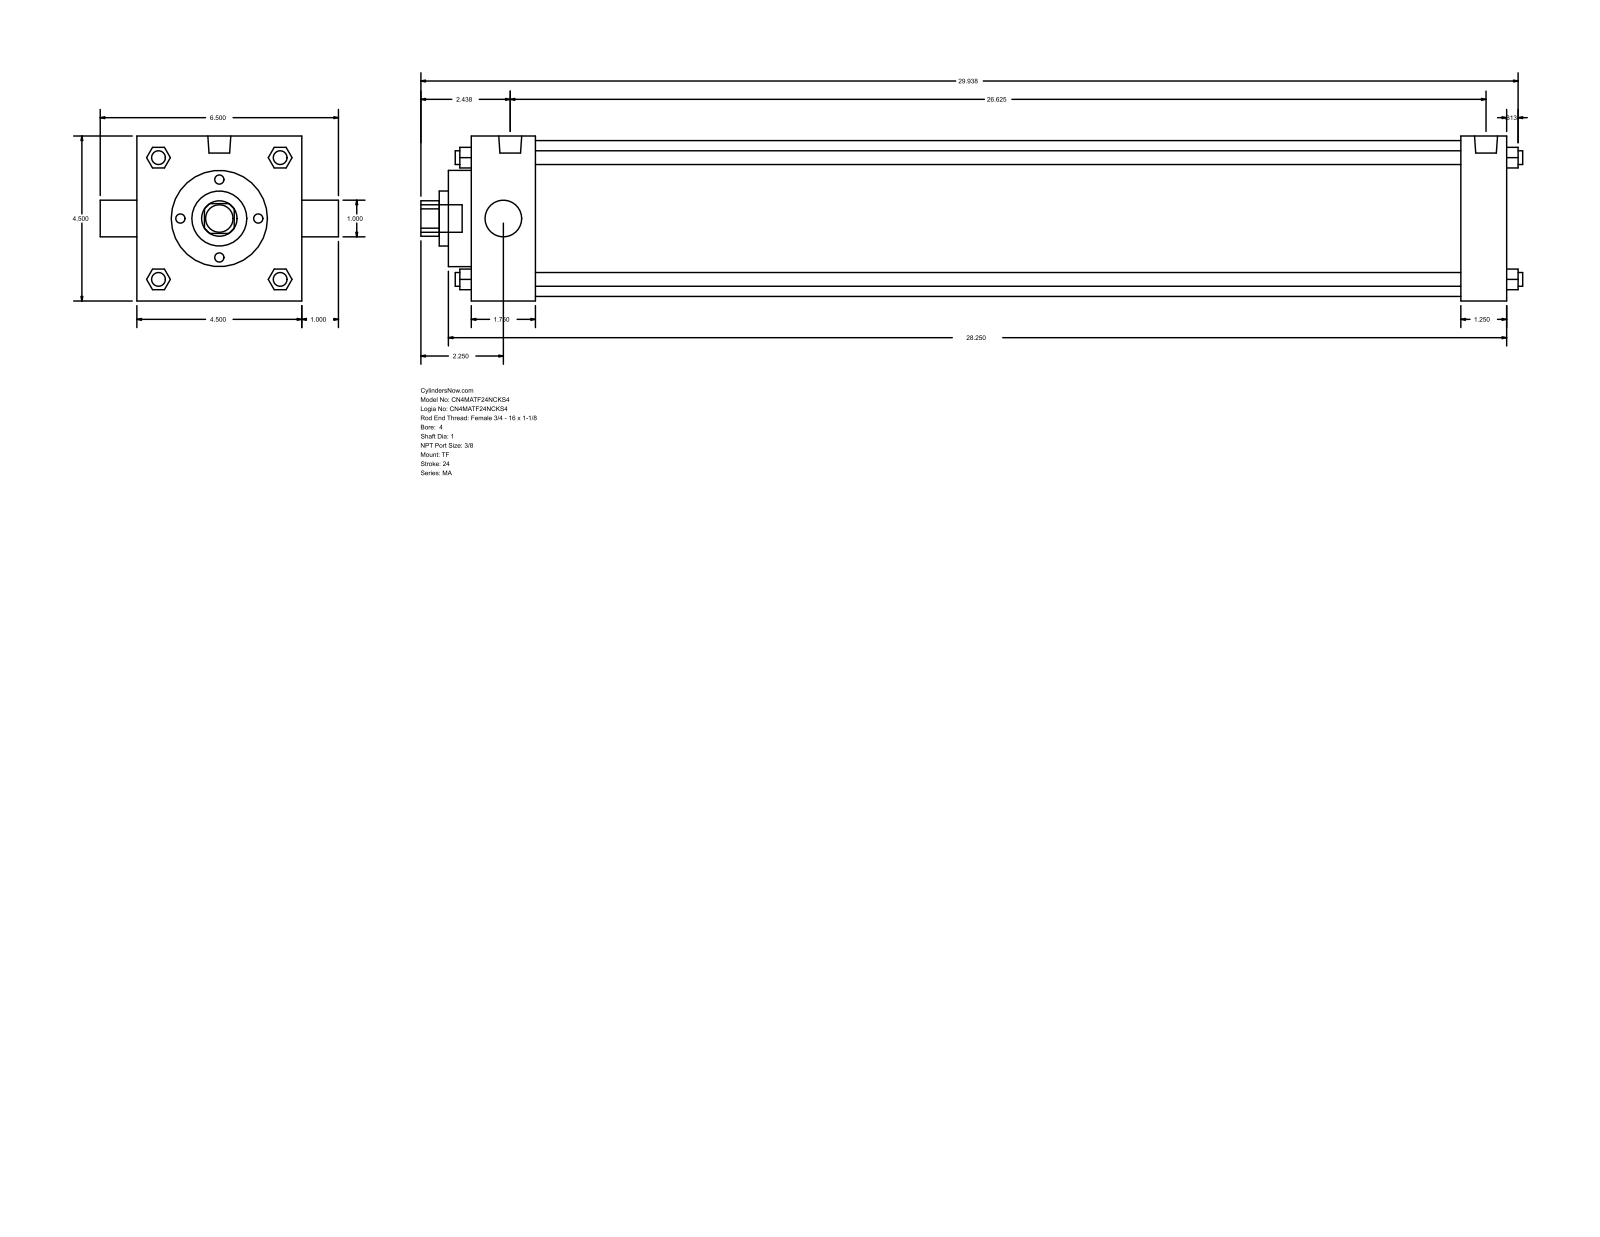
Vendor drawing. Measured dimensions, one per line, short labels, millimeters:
name: MA_TF__0400_1
written by: GSSL Pune (CONFIG_CONTROL_DESIGN)
unit: mm
bodies: 0 solids, 122 faces (93 planar, 29 cylindrical, 0 other)
size: 763.59 × 165.1 × 114.3
holes: 2× ⌀25.4, 1× ⌀38.1, 1× ⌀66.67, 1× ⌀107.95
bosses: 4× ⌀9.53, 3× ⌀11.11, 2× ⌀15.93, 1× ⌀19.05
rounds: 1× R12.29
face distances: 114.3, 717.56, 685.81, 31.75, 44.46, 641.35, 673.1, 15.87, 60.33, 701.68
